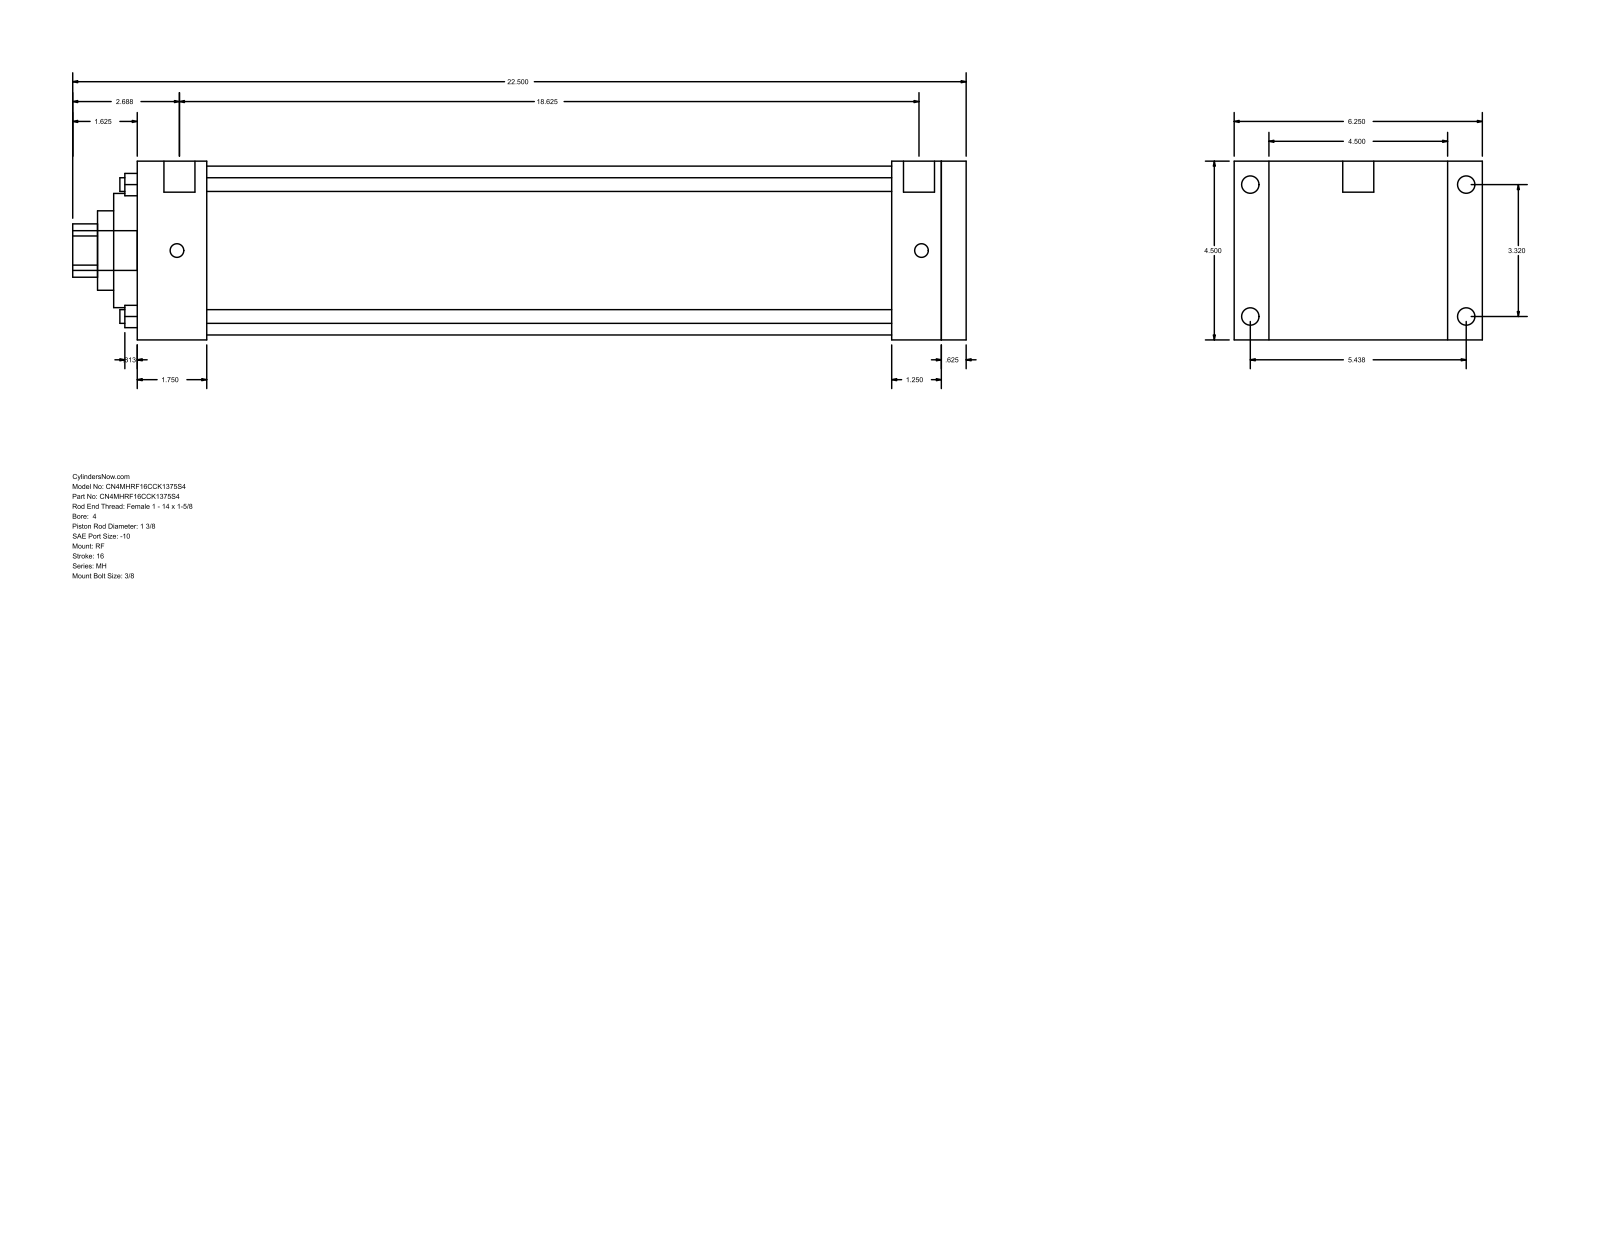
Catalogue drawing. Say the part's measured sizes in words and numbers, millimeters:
The part is named "MH_RF__0400_1.375". Its 3-D file was written by "GSSL Pune (CONFIG_CONTROL_DESIGN)". It is 0 solids with 94 faces: 65 planar, 29 cylindrical and 0 other. Overall it measures 571.5 by 158.75 by 114.3 millimeters. Round holes: 4 of diameter 8.76, 1 of diameter 34.92, 1 of diameter 50.8, 1 of diameter 73.03, 1 of diameter 107.95. Round bosses or shafts: 4 of diameter 11.13, 4 of diameter 8.73, 2 of diameter 19.84, 1 of diameter 25.4. Partial cylindrical surfaces (rounded edges, fillets, slot ends): 1 of radius 17.06. The main face-to-face distances are 114.3, 530.23, 15.88, 514.35, 44.45, 469.9, 485.78, 482.61, 438.16, 31.74. The hole center spacings are 59.62, 84.32, 119.25.
